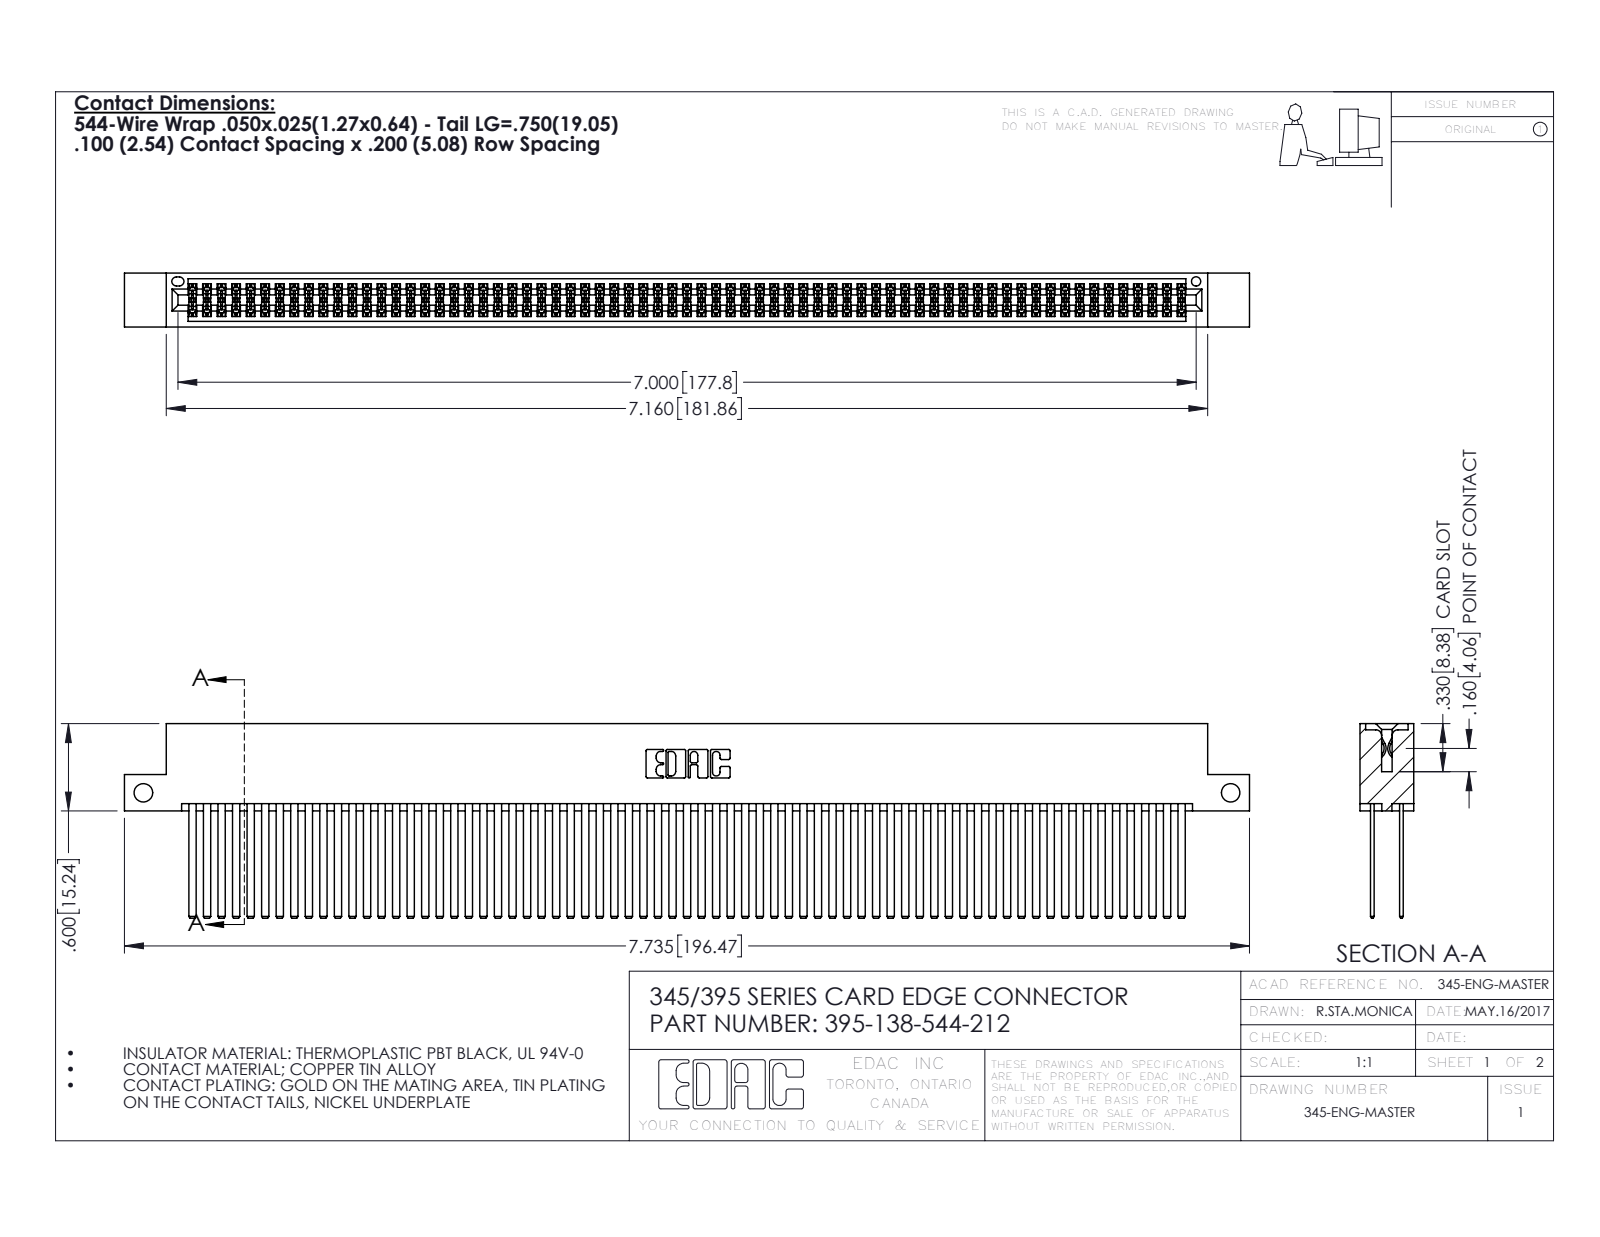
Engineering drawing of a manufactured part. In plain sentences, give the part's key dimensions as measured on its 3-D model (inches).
The part is named "345 Part_Flush Mounting Lugs - Side Mount; 395-138-544-212; 345-292-001_345-293-144". Its 3-D file was written by "SolidWorks 2016 (CONFIG_CONTROL_DESIGN)". It is 139 solids with 6198 faces: 4082 planar, 2116 cylindrical and 0 other. Overall it measures 7.735 by 1.337 by 0.37 inches. Its volume is 1.293 cubic inches and its surface area 57.92 square inches. Round holes: 2 of diameter 0.128, 1 of diameter 0.064. Partial cylindrical surfaces (rounded edges, fillets, slot ends): 207 of radius 0.006, 22 of radius 0.01, 6 of radius 0.007, 6 of radius 0.031, 3 of radius 0.026, 2 of radius 0.014, 2 of radius 0.019, 2 of radius 0.022. The main face-to-face distances are 0.2, 0.025, 0.298, 0.072, 0.098, 0.272, 0.225, 0.175, 0.37, 0.05. The hole center spacings are 7.475.
